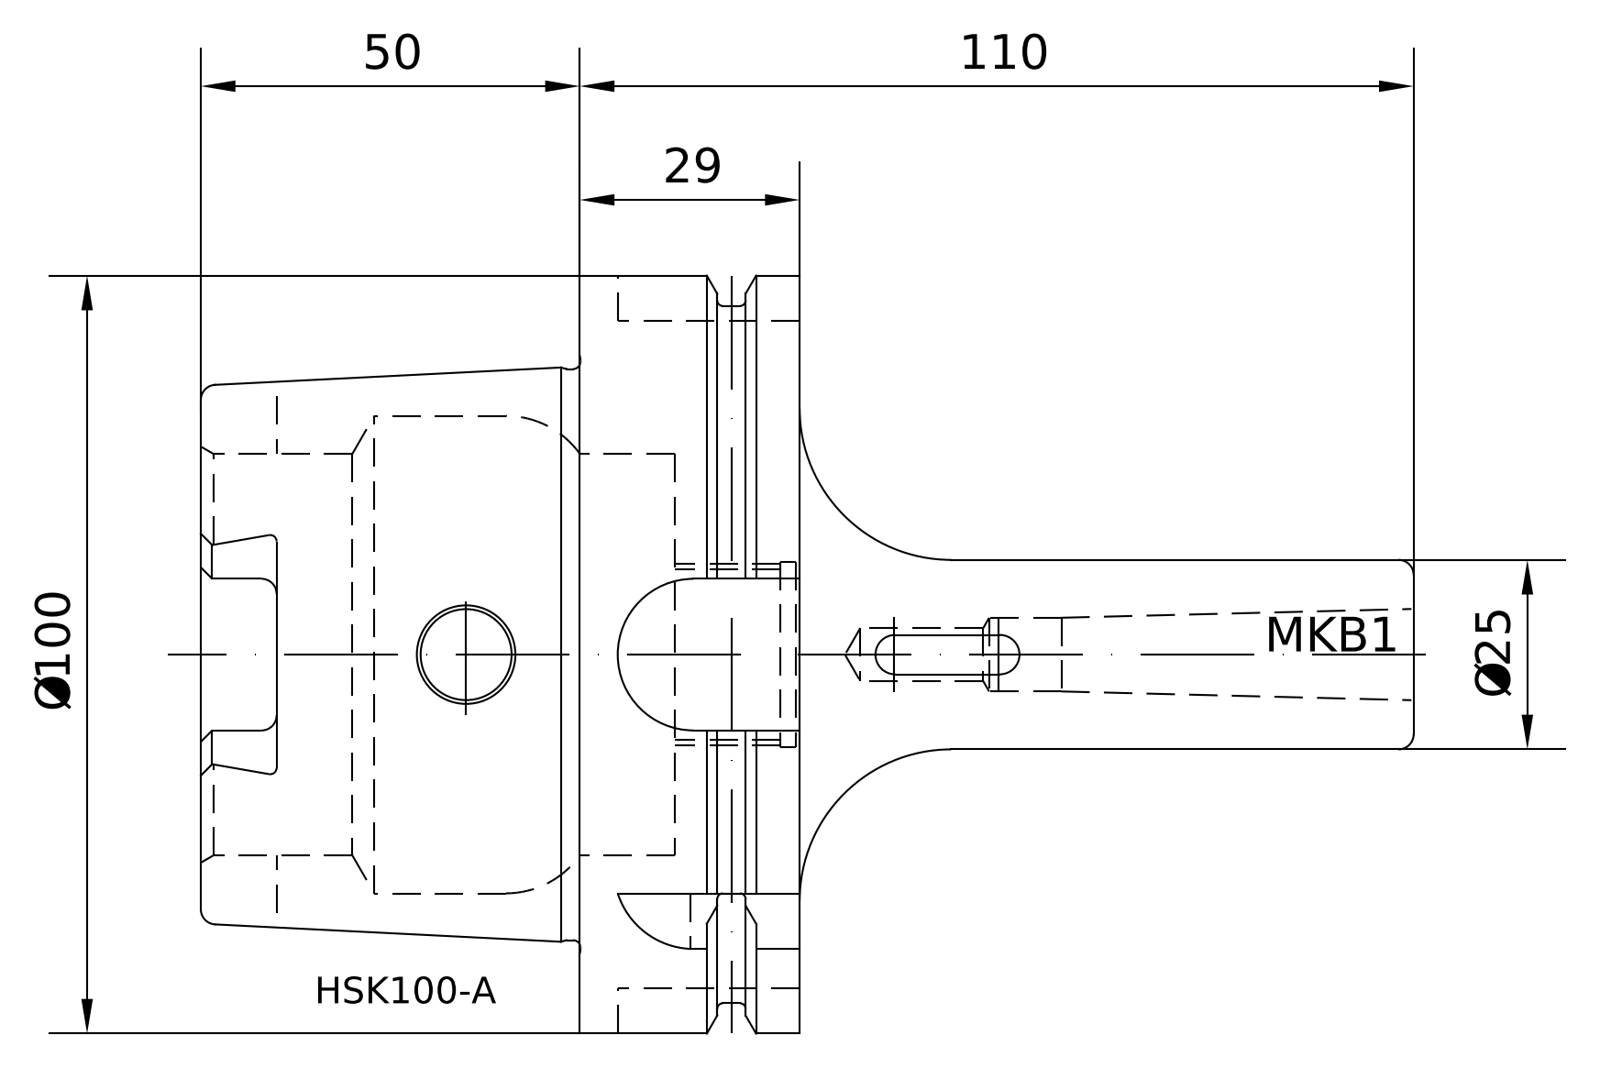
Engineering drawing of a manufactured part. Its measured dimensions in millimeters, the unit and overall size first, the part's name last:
Units: millimetres
Overall size (bounding box): 160 × 100 × 100
Round holes (diameter × count): ⌀9.7 ×1, ⌀10 ×1, ⌀12 ×1, ⌀22.5 ×1, ⌀24 ×1, ⌀24.32 ×1, ⌀24.5 ×1, ⌀53 ×1, ⌀63 ×1
Round bosses / shafts (diameter × count): ⌀100 ×1, ⌀92 ×1, ⌀75.36 ×1, ⌀25 ×1
Partial cylindrical surfaces — rounded edges, fillets, slot ends (radius × count): R2 ×6, R5 ×4, R8 ×1, R10 ×1, R11 ×1
Main face-to-face distances: 29, 12.5, 16.5, 50, 62.5, 79, 88, 78.5, 28.5, 16
Volume: 297 921 mm³ · Surface area: 57 906 mm²
Bodies: 1 solid, 174 faces (50 planar, 51 cylindrical, 73 other)
Part name (STEP PRODUCT): A100-080-01
STEP written by: PRO/ENGINEER BY PARAMETRIC TECHNOLOGY CORPORATION, 2010430 (CONFIG_CONTROL_DESIGN)
